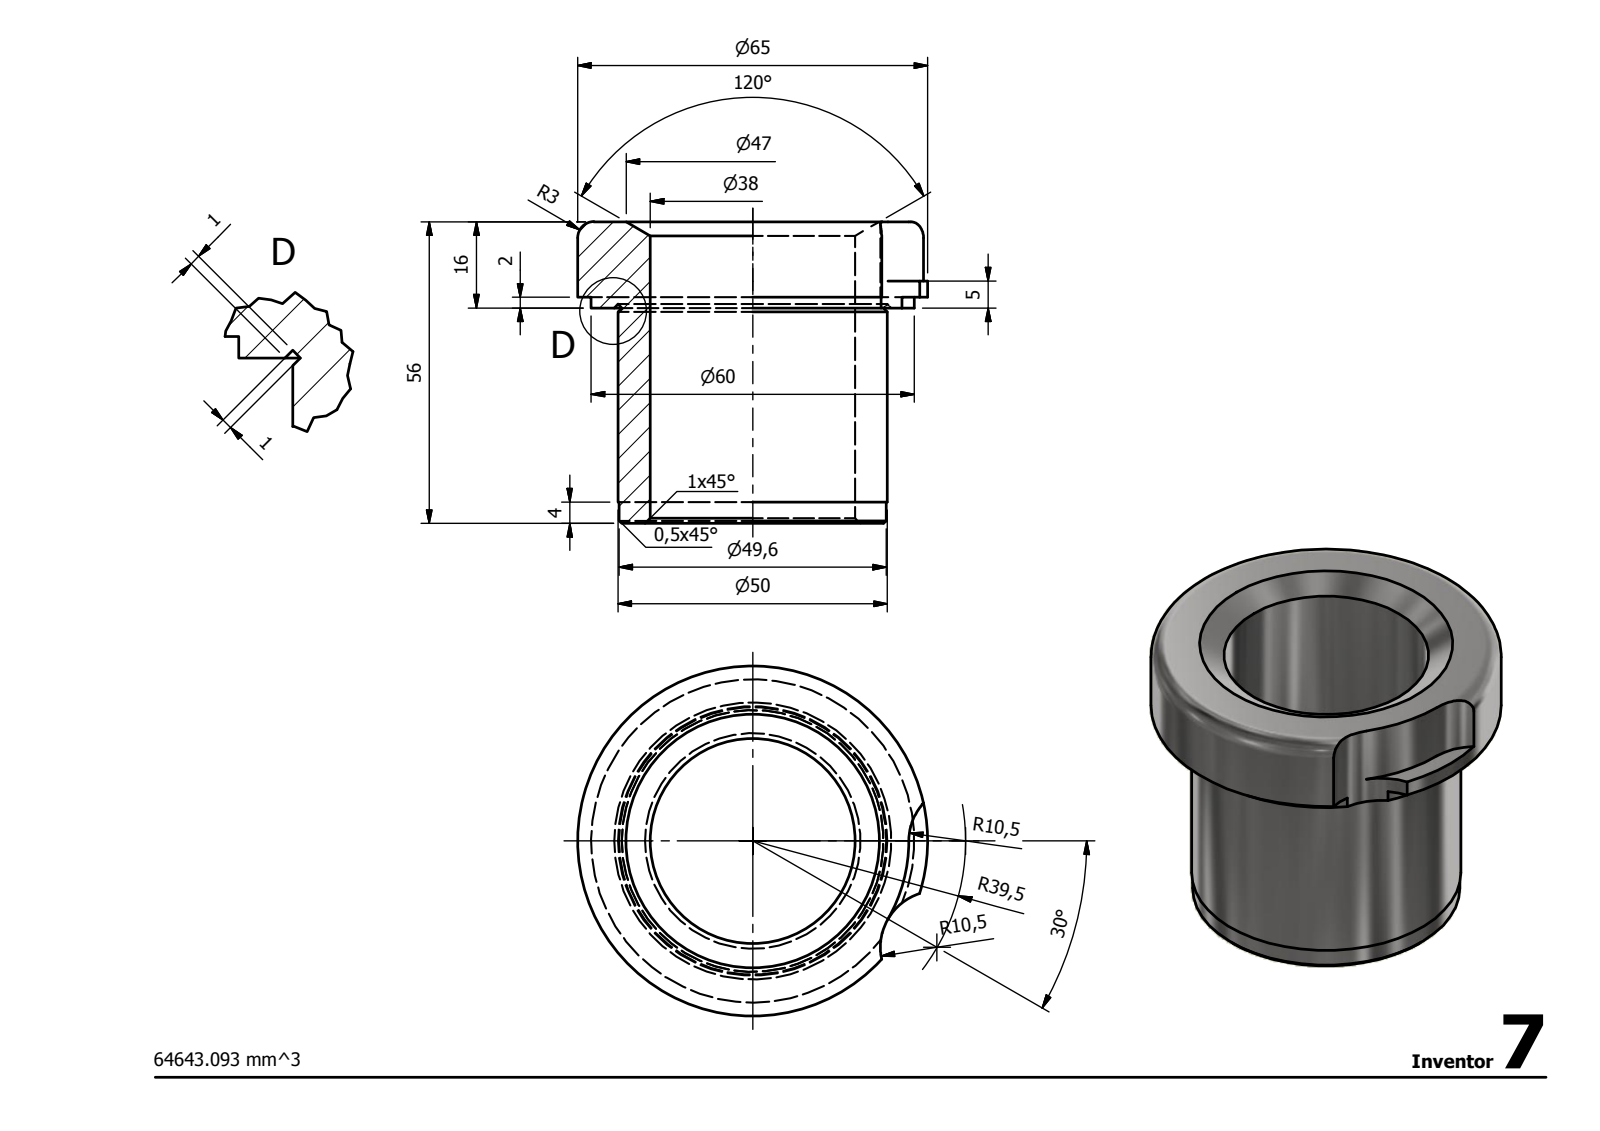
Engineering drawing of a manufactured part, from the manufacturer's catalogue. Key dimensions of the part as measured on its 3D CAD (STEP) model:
STEP written by: Autodesk Inventor 2014 (AUTOMOTIVE_DESIGN)
Units: millimetres
Bodies: 1 solid, 21 faces (6 planar, 8 cylindrical, 7 other)
Overall size (bounding box): 65 × 65 × 56
Volume: 64 633 mm³ · Surface area: 20 181 mm²
Round holes (diameter × count): ⌀38 ×1
Round bosses / shafts (diameter × count): ⌀65 ×1, ⌀60 ×1, ⌀50 ×1, ⌀49.6 ×1
Partial cylindrical surfaces — rounded edges, fillets, slot ends (radius × count): R10.5 ×2, R29 ×1
Main face-to-face distances: 16, 40, 56, 42, 2, 14, 45, 5, 3, 11
